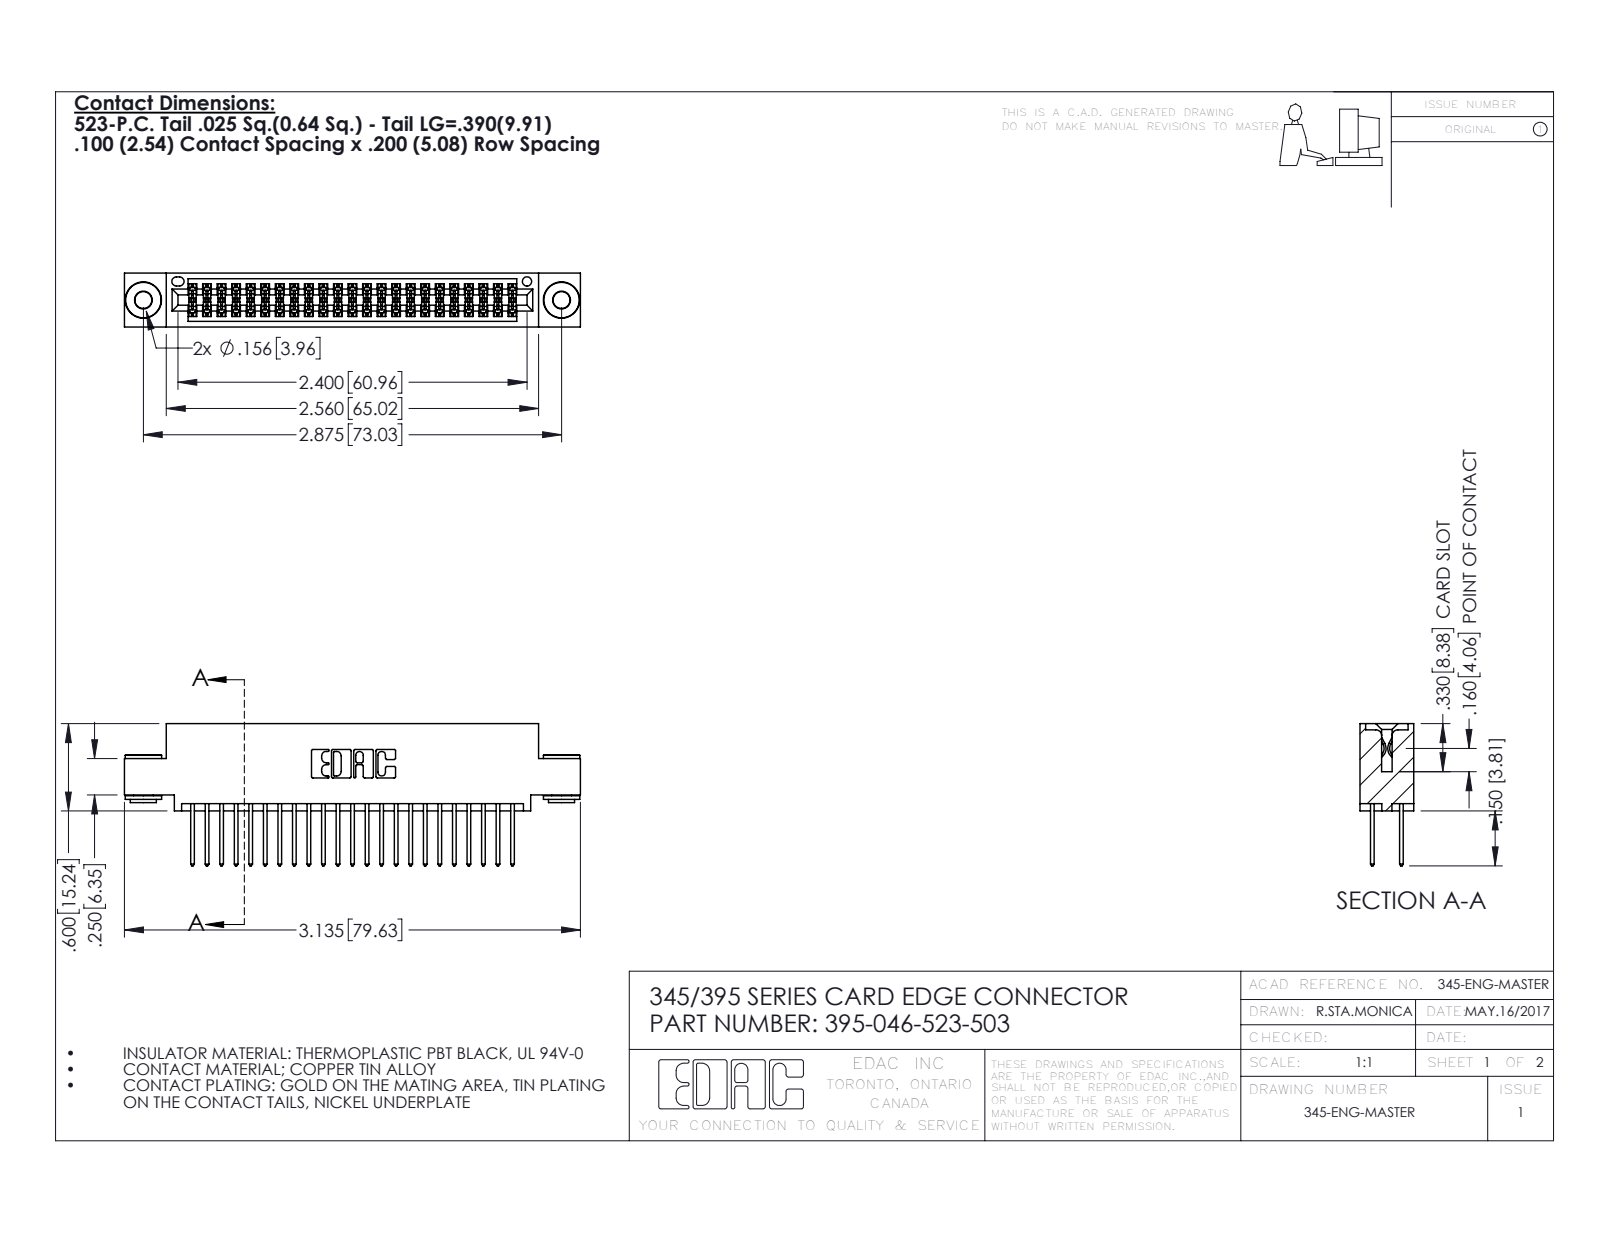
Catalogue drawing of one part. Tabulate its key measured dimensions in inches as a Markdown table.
| quantity | value |
| --- | --- |
| part name | 345-250-002_345-250-002-102; 345-292-001_345-293-123; 395-046-523-503; 345 Part_0.110 Offset - 0.156 Dia-TH |
| STEP written by | SolidWorks 2016 (CONFIG_CONTROL_DESIGN) |
| units | inches |
| bodies | 49 solids, 2468 faces (1612 planar, 848 cylindrical, 8 other) |
| overall size | 3.135 × 0.977 × 0.37 |
| volume | 0.464 in³ |
| surface area | 17.96 in² |
| round holes (diameter × count) | 0.116 × 2, 0.156 × 2, 0.064 × 1 |
| round bosses / shafts (diameter × count) | 0.25 × 2, 0.18 × 2, 0.136 × 2 |
| partial cylindrical surfaces (radius × count) | 0.006 × 69, 0.01 × 46, 0.01 × 22, 0.007 × 6, 0.031 × 6, 0.026 × 3, 0.014 × 2, 0.019 × 2 |
| main face-to-face distances | 0.072, 0.298, 0.2, 0.025, 0.098, 0.272, 0.37, 0.225, 0.175, 0.149 |
| hole center spacings | 0.27, 2.641, 2.875 |
